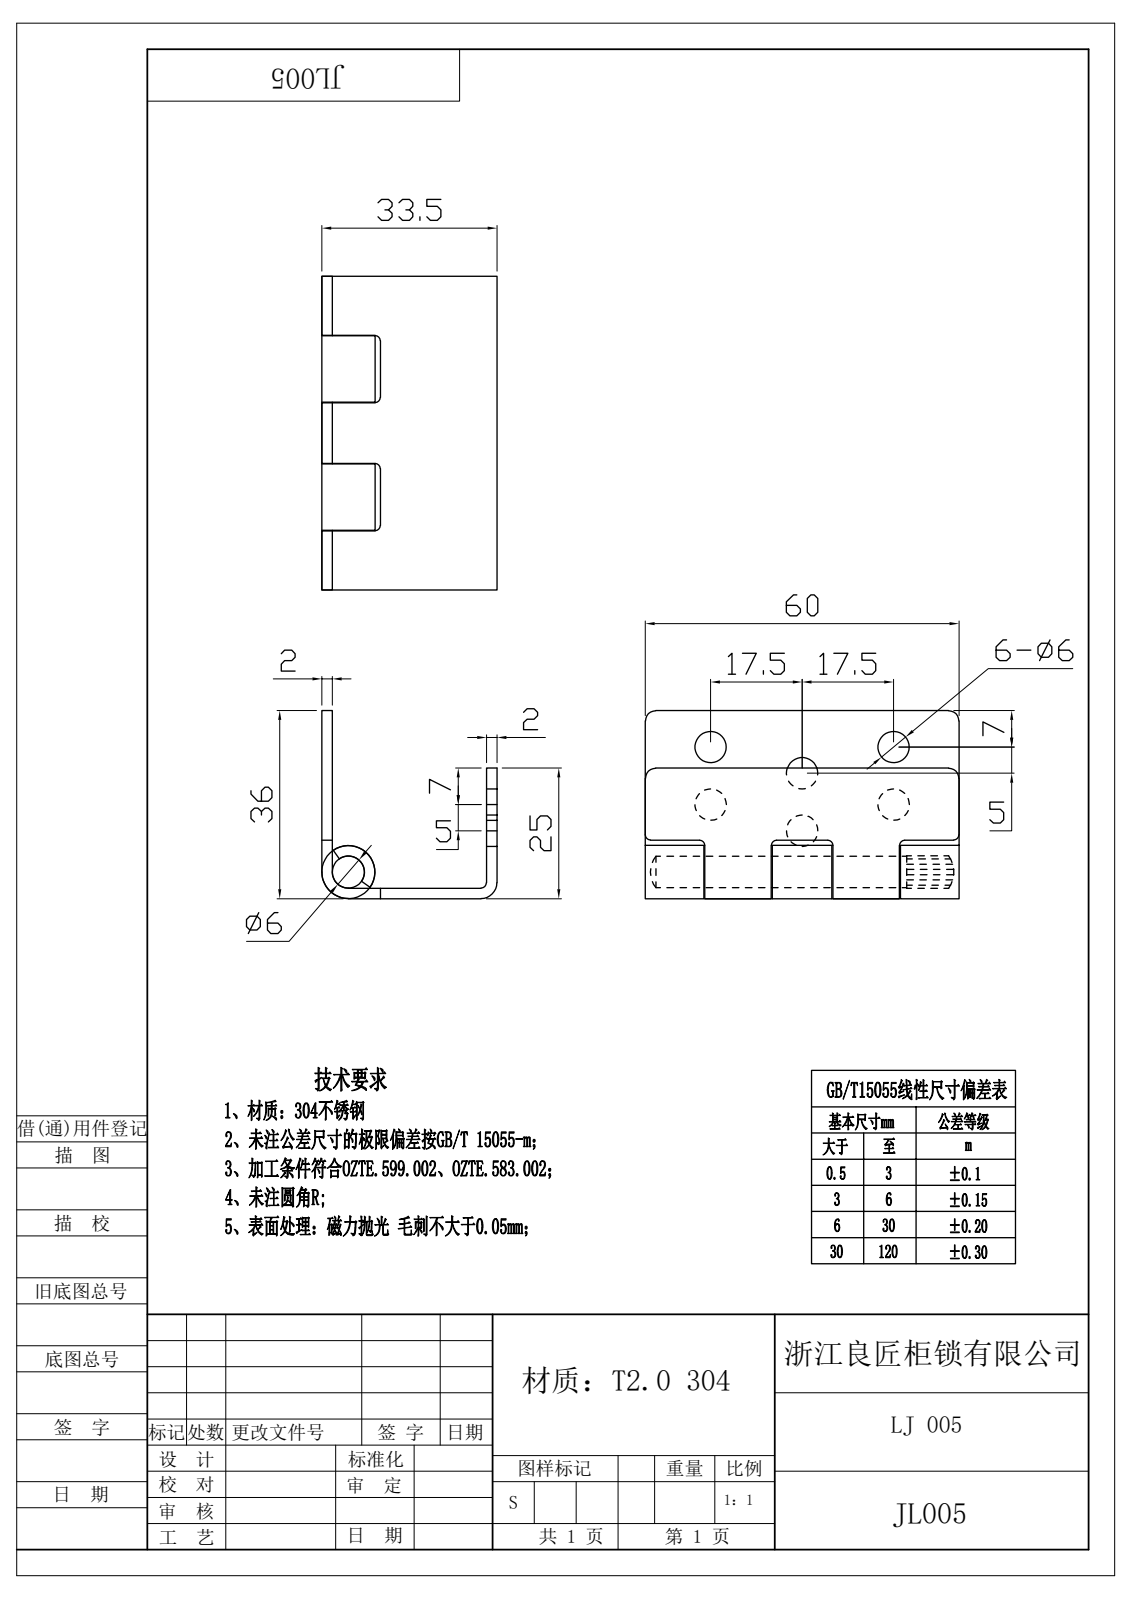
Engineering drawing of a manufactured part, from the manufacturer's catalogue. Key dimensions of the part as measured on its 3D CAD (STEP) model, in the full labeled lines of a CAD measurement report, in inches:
STEP written by: Rhino 8.5 (CONFIG_CONTROL_DESIGN)
Units: inches
Bodies: 3 solids, 98 faces (30 planar, 46 cylindrical, 22 other)
Overall size (bounding box): 2.362 × 1.417 × 1.319
Volume: 0.784 in³ · Surface area: 21.61 in²
Round holes (diameter × count): ⌀0.236 ×6, ⌀0.244 ×1
Round bosses / shafts (diameter × count): ⌀0.402 ×1
Partial cylindrical surfaces — rounded edges, fillets, slot ends (radius × count): R0.02 ×6, R0.039 ×6, R0.079 ×4, R0.041 ×1, R0.12 ×1
Main face-to-face distances: 0.079, 1.24, 1.319, 1.161, 2.362, 0.441, 0.906, 0.984, 0.433, 1.339
Hole centre spacings: 0.717, 0.433, 0.728, 0.933, 1.378, 1.444
